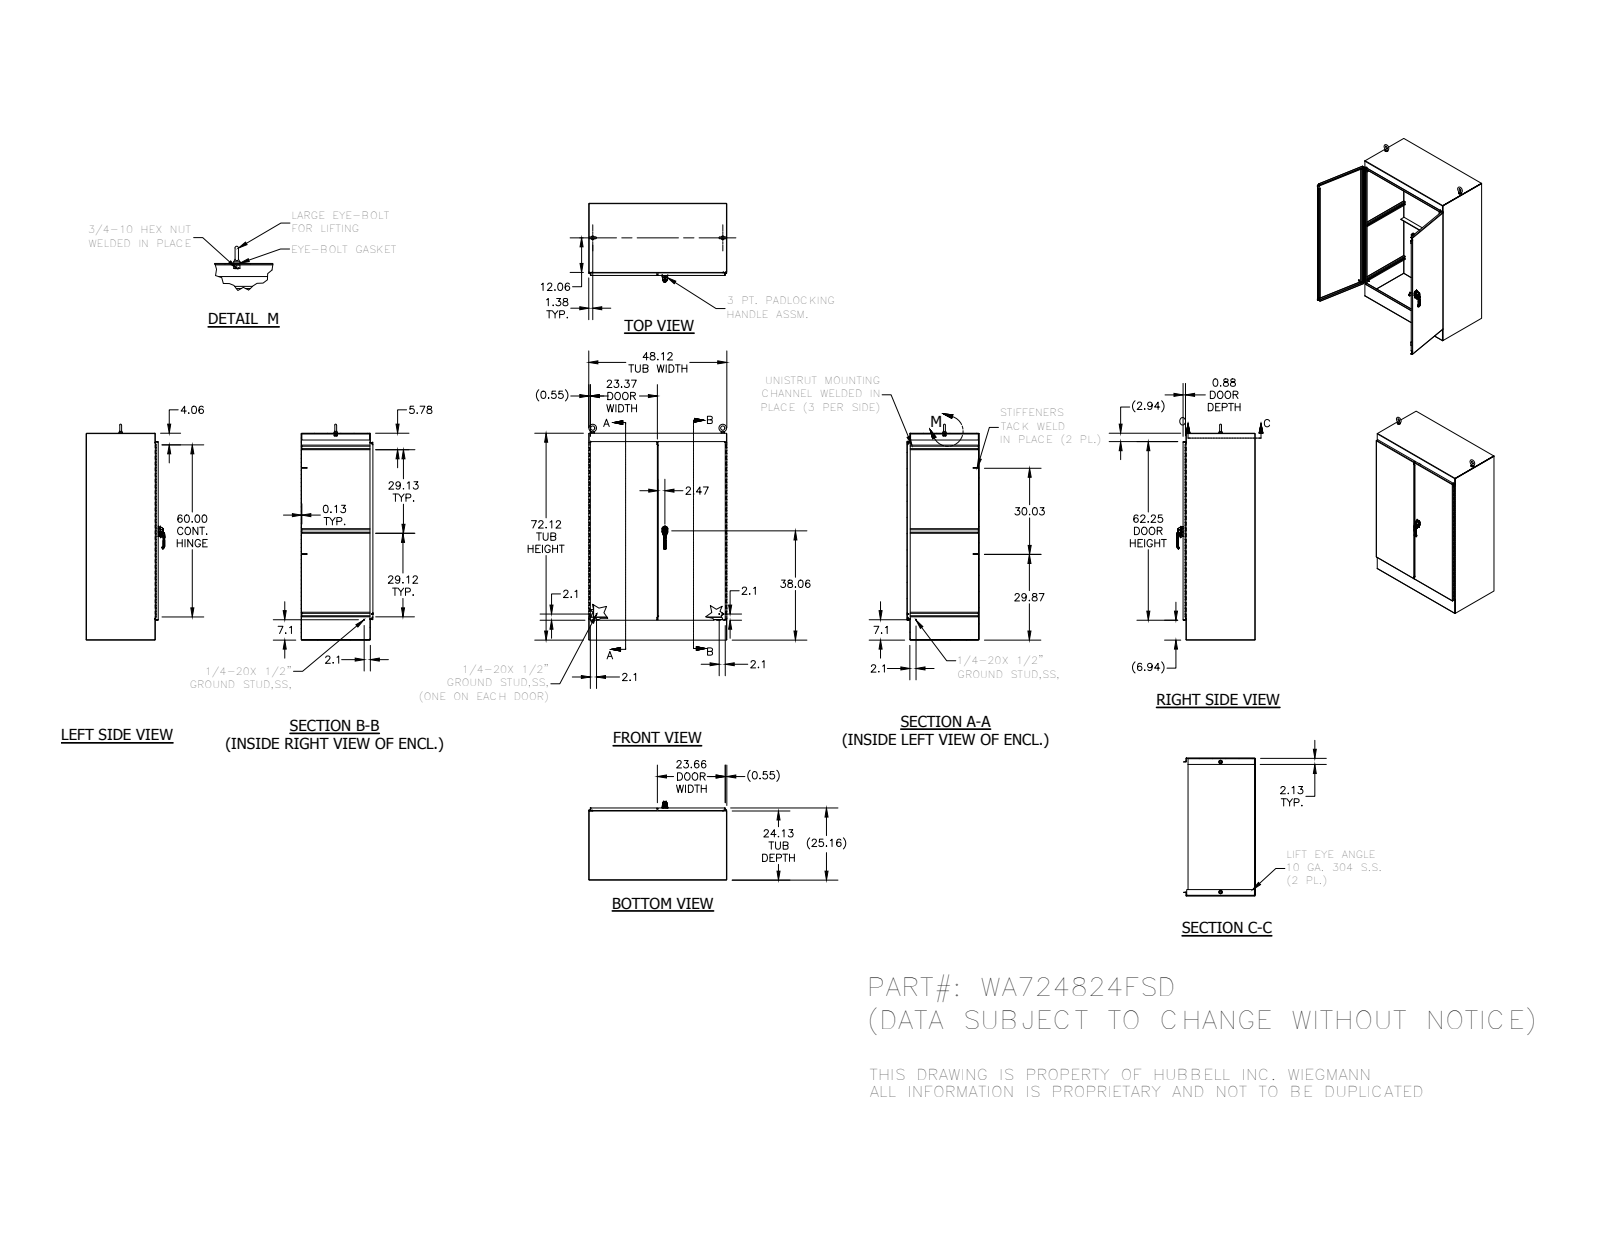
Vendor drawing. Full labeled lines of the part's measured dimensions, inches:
Part name (STEP PRODUCT): FUN00103; HFW3025; 316298; 349132 (+8 more)
STEP written by: Autodesk Inventor 2014 (AUTOMOTIVE_DESIGN)
Units: inches
Bodies: 66 solids, 3780 faces (1777 planar, 1263 cylindrical, 740 other)
Overall size (bounding box): 75.248 × 48.139 × 27.431
Volume: 1 883 in³ · Surface area: 30 330 in²
Round holes (diameter × count): ⌀0.276 ×8, ⌀0.2 ×4, ⌀0.213 ×3, ⌀0.236 ×3, ⌀0.28 ×3, ⌀0.125 ×2, ⌀0.241 ×2, ⌀0.25 ×2, ⌀0.252 ×2, ⌀0.4 ×2, ⌀0.407 ×2, ⌀0.413 ×2
Round bosses / shafts (diameter × count): ⌀0.25 ×5, ⌀0.337 ×3, ⌀1.25 ×2, ⌀1.12 ×2, ⌀1 ×2, ⌀0.75 ×2, ⌀0.563 ×2, ⌀0.526 ×2
Partial cylindrical surfaces — rounded edges, fillets, slot ends (radius × count): R0.02 ×164, R0.012 ×84, R0.031 ×24, R0.156 ×21, R0.019 ×19, R0.01 ×16, R0.079 ×15, R0.05 ×14
Main face-to-face distances: 0.125, 48, 0.125, 25.038, 24.913, 25.163, 25.038, 72, 47.875, 48.125
Hole centre spacings: 0.236, 0.256, 0.381, 0.381, 0.383, 0.492, 0.492, 0.762
